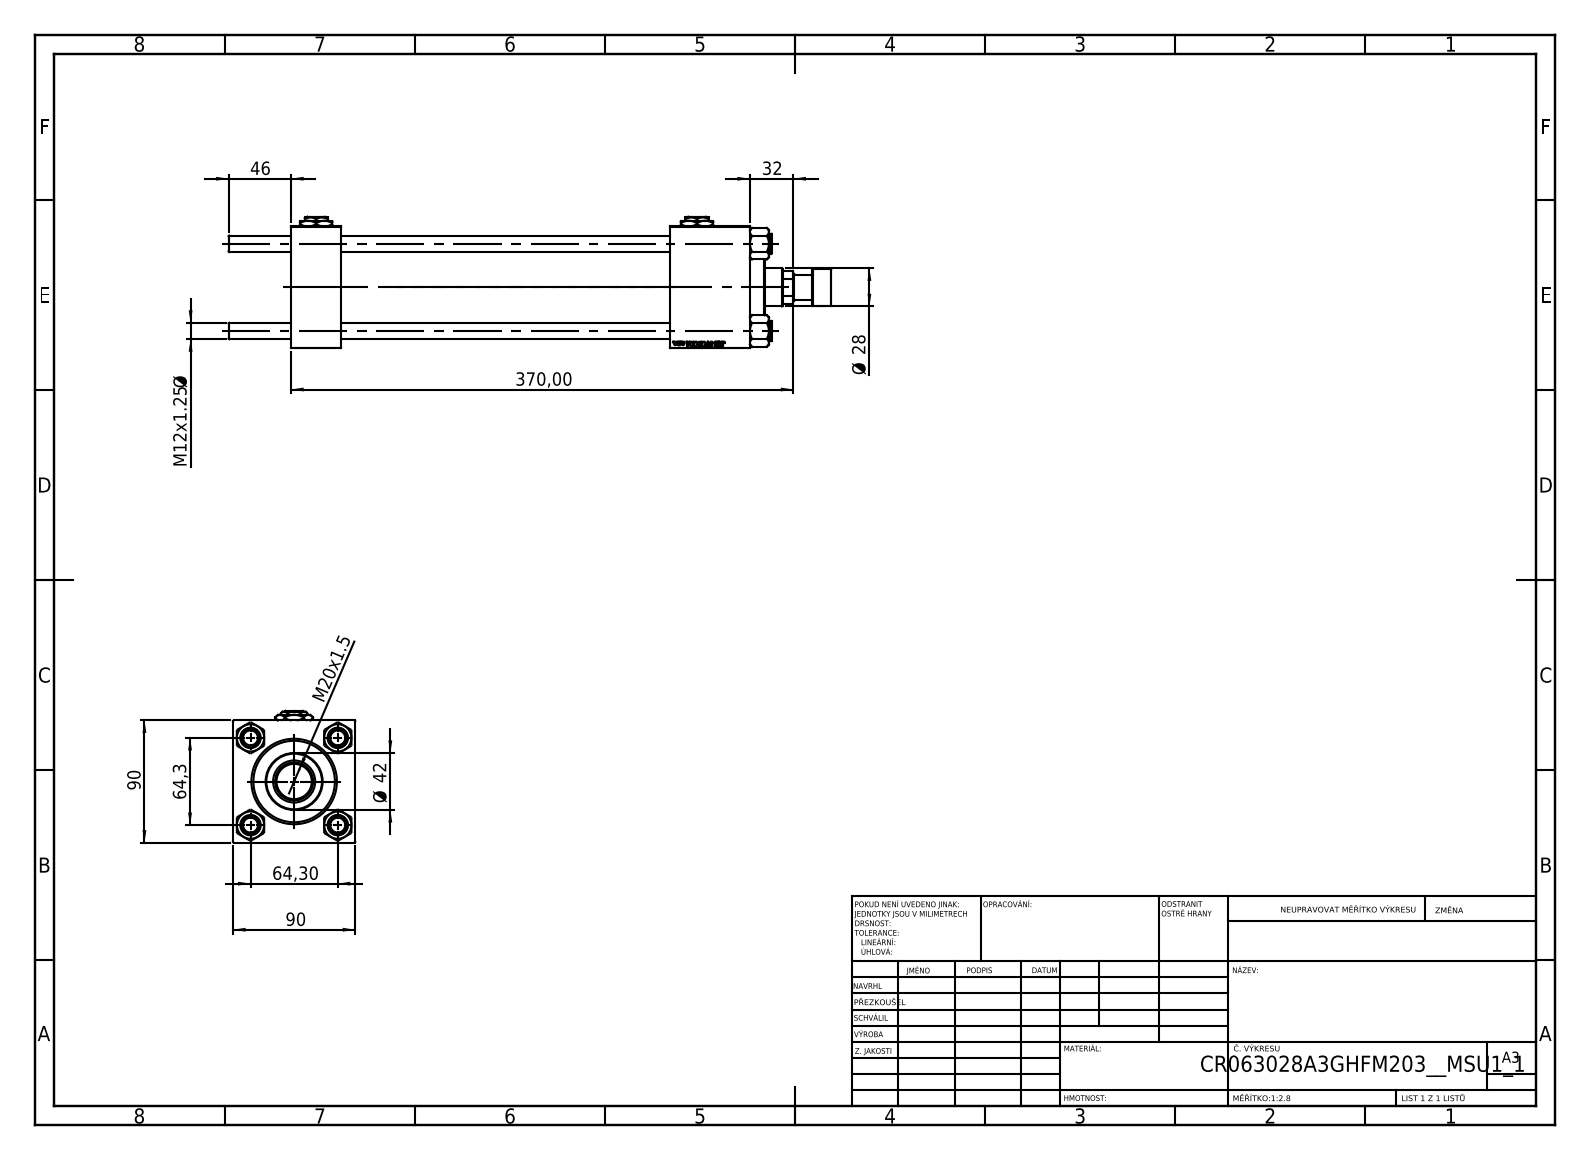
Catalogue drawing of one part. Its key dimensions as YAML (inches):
part_name: "Zatka_pro_OIL_PORT; NUT_M5; V215CR_ROD_END_F; V215_VC_A (+3 more)"
step_written_by: "SolidWorks 2019 (CONFIG_CONTROL_DESIGN)"
units: inches
bodies: {solids: 14, faces: 1247, planar: 571, cylindrical: 92, other: 584}
overall_size: [17.48, 3.819, 3.543]
volume: 79.09
surface_area: 500.5
round_holes:
  - {diameter: 0.472, count: 4}
  - {diameter: 0.276, count: 2}
  - {diameter: 0.825, count: 2}
  - {diameter: 1.181, count: 2}
  - {diameter: 0.728, count: 1}
  - {diameter: 1.102, count: 1}
  - {diameter: 1.22, count: 1}
  - {diameter: 1.969, count: 1}
  - {diameter: 2.362, count: 1}
  - {diameter: 2.48, count: 1}
round_bosses_or_shafts:
  - {diameter: 0.591, count: 4}
  - {diameter: 2.717, count: 1}
  - {diameter: 1.654, count: 1}
  - {diameter: 1.063, count: 1}
  - {diameter: 0.709, count: 1}
face_to_face_distances: [3.543, 1.457, 13.307, 11.85, 2.323, 10.984, 9.528, 12.177, 10.72, 1.193]
hole_center_spacings: [1.79, 2.531, 3.58, 11.043]
